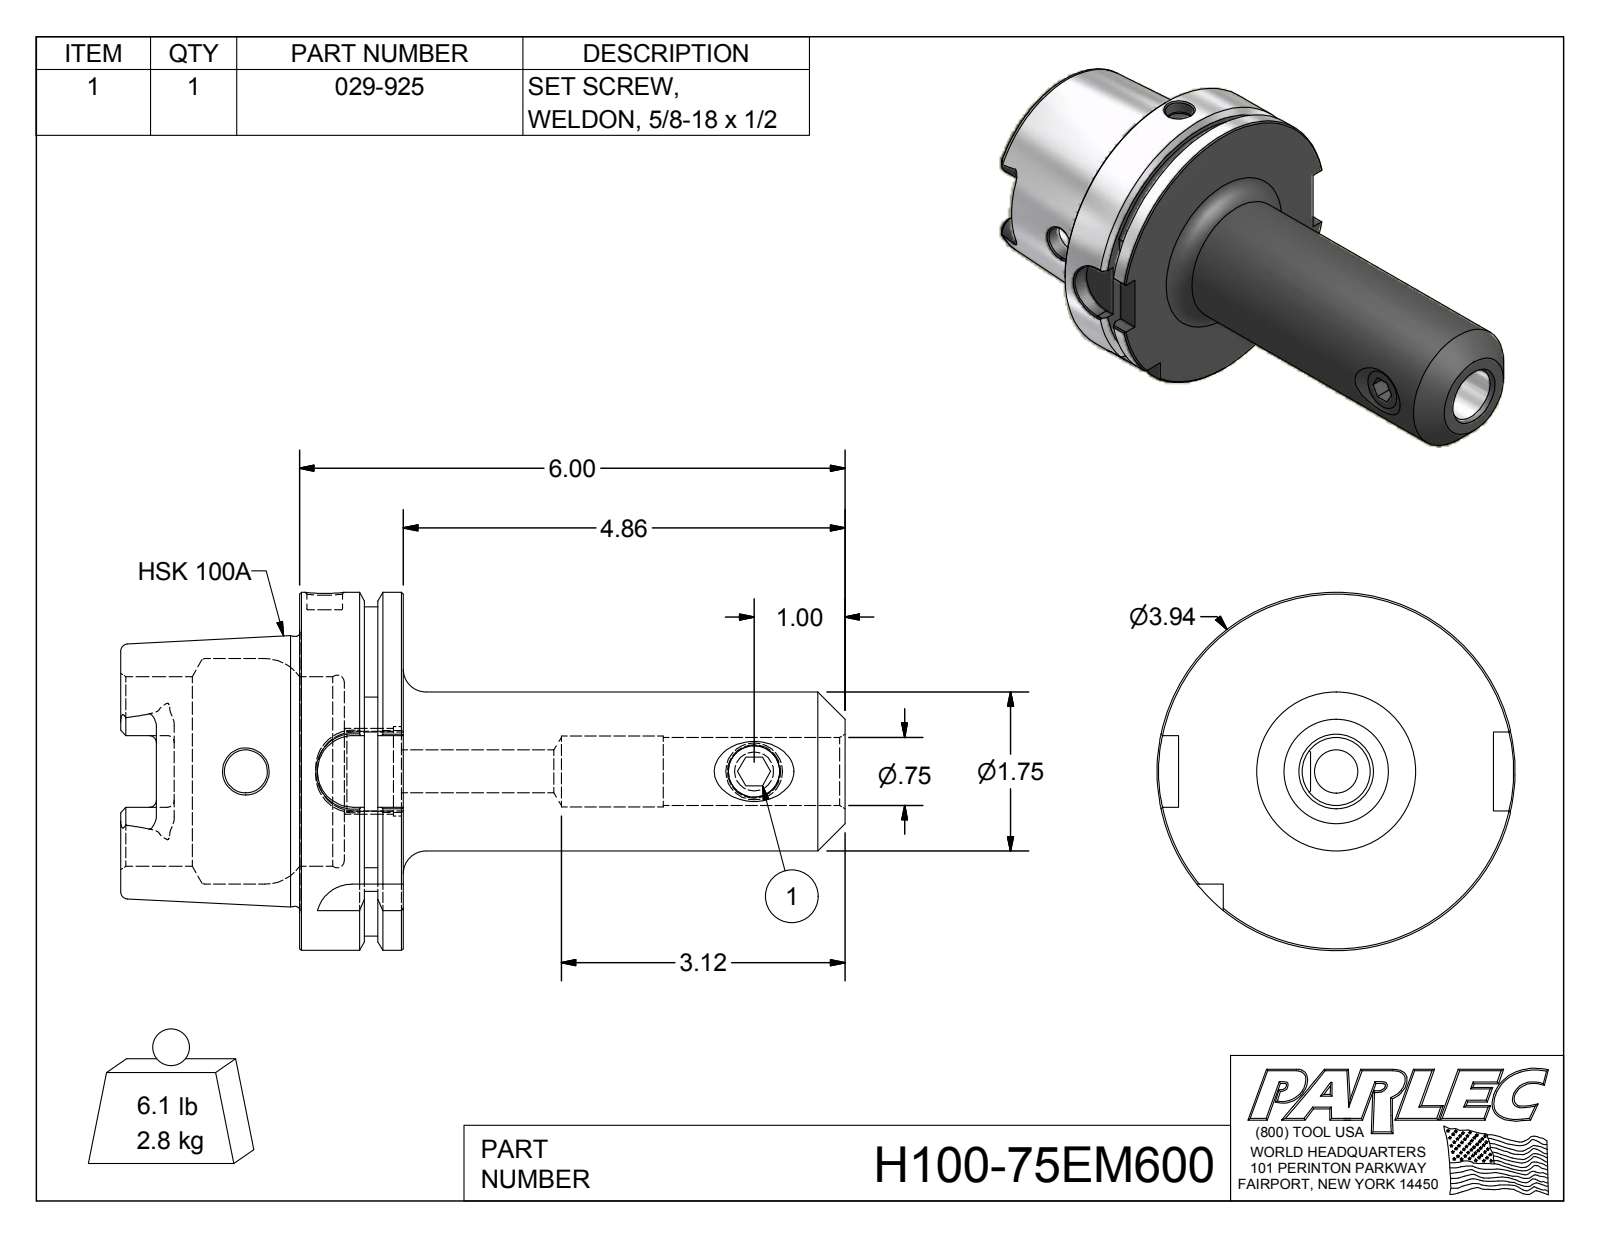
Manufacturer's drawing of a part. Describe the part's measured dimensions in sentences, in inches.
The part is named "H100-75EM600; 029-925". Its 3-D file was written by "Autodesk Inventor 2012 (AUTOMOTIVE_DESIGN)". It is 2 solids with 140 faces: 53 planar, 36 cylindrical and 51 other. Overall it measures 7.969 by 3.937 by 3.937 inches. Its volume is 25.27 cubic inches and its surface area 114.5 square inches. Round holes: 2 of diameter 0.472, 1 of diameter 0.394, 1 of diameter 0.565, 1 of diameter 0.75, 1 of diameter 0.78, 1 of diameter 0.881, 1 of diameter 0.985, 1 of diameter 2.087, 1 of diameter 2.48. Round bosses or shafts: 1 of diameter 3.937, 1 of diameter 2.967, 1 of diameter 1.75, 1 of diameter 0.625. Partial cylindrical surfaces (rounded edges, fillets, slot ends): 6 of radius 0.079, 4 of radius 0.192, 4 of radius 0.394, 1 of radius 1.811. The main face-to-face distances are 1.142, 0.492, 0.65, 1.969, 2.461, 3.11, 2.83, 0.861, 0.369, 0.28. The hole center spacings are 5.591.
